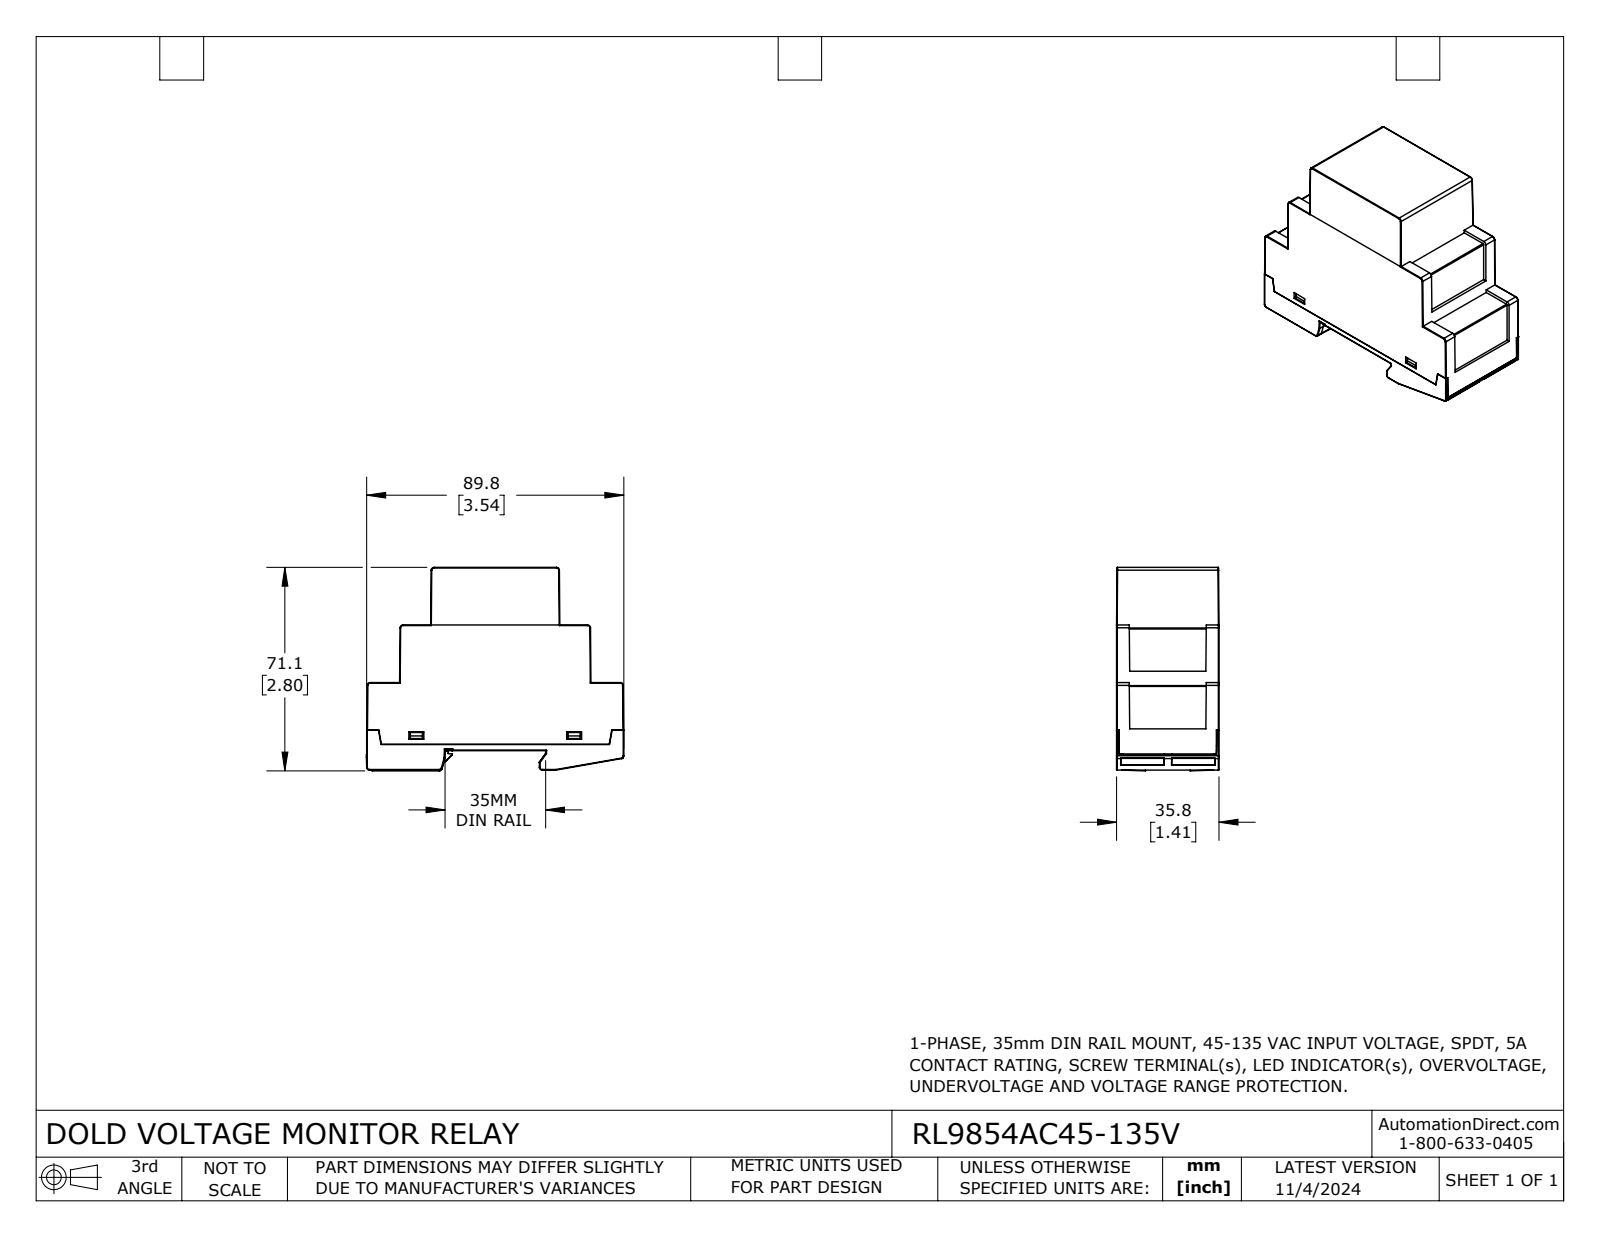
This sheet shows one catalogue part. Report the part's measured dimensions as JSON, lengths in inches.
{"part_name": "RL9854AC45-135V", "step_written_by": "SolidWorks 2023 (CONFIG_CONTROL_DESIGN)", "units": "inches", "bodies": {"solids": 2, "faces": 643, "planar": 492, "cylindrical": 113, "other": 38}, "overall_size": [3.538, 2.799, 1.409], "volume_in3": 9.342, "surface_area_in2": 55.38, "round_bosses_or_shafts": [[0.098, 2], [0.315, 1]], "partial_cylinders_radius": [[0.008, 42], [0.039, 14], [0.02, 11], [0.004, 6], [0.012, 4], [0.079, 4], [0.011, 1], [0.016, 1]], "face_to_face_distances": [1.409, 0.217, 2.52, 0.035, 0.085, 2.435, 2.219, 0.301, 0.824, 1.374]}
